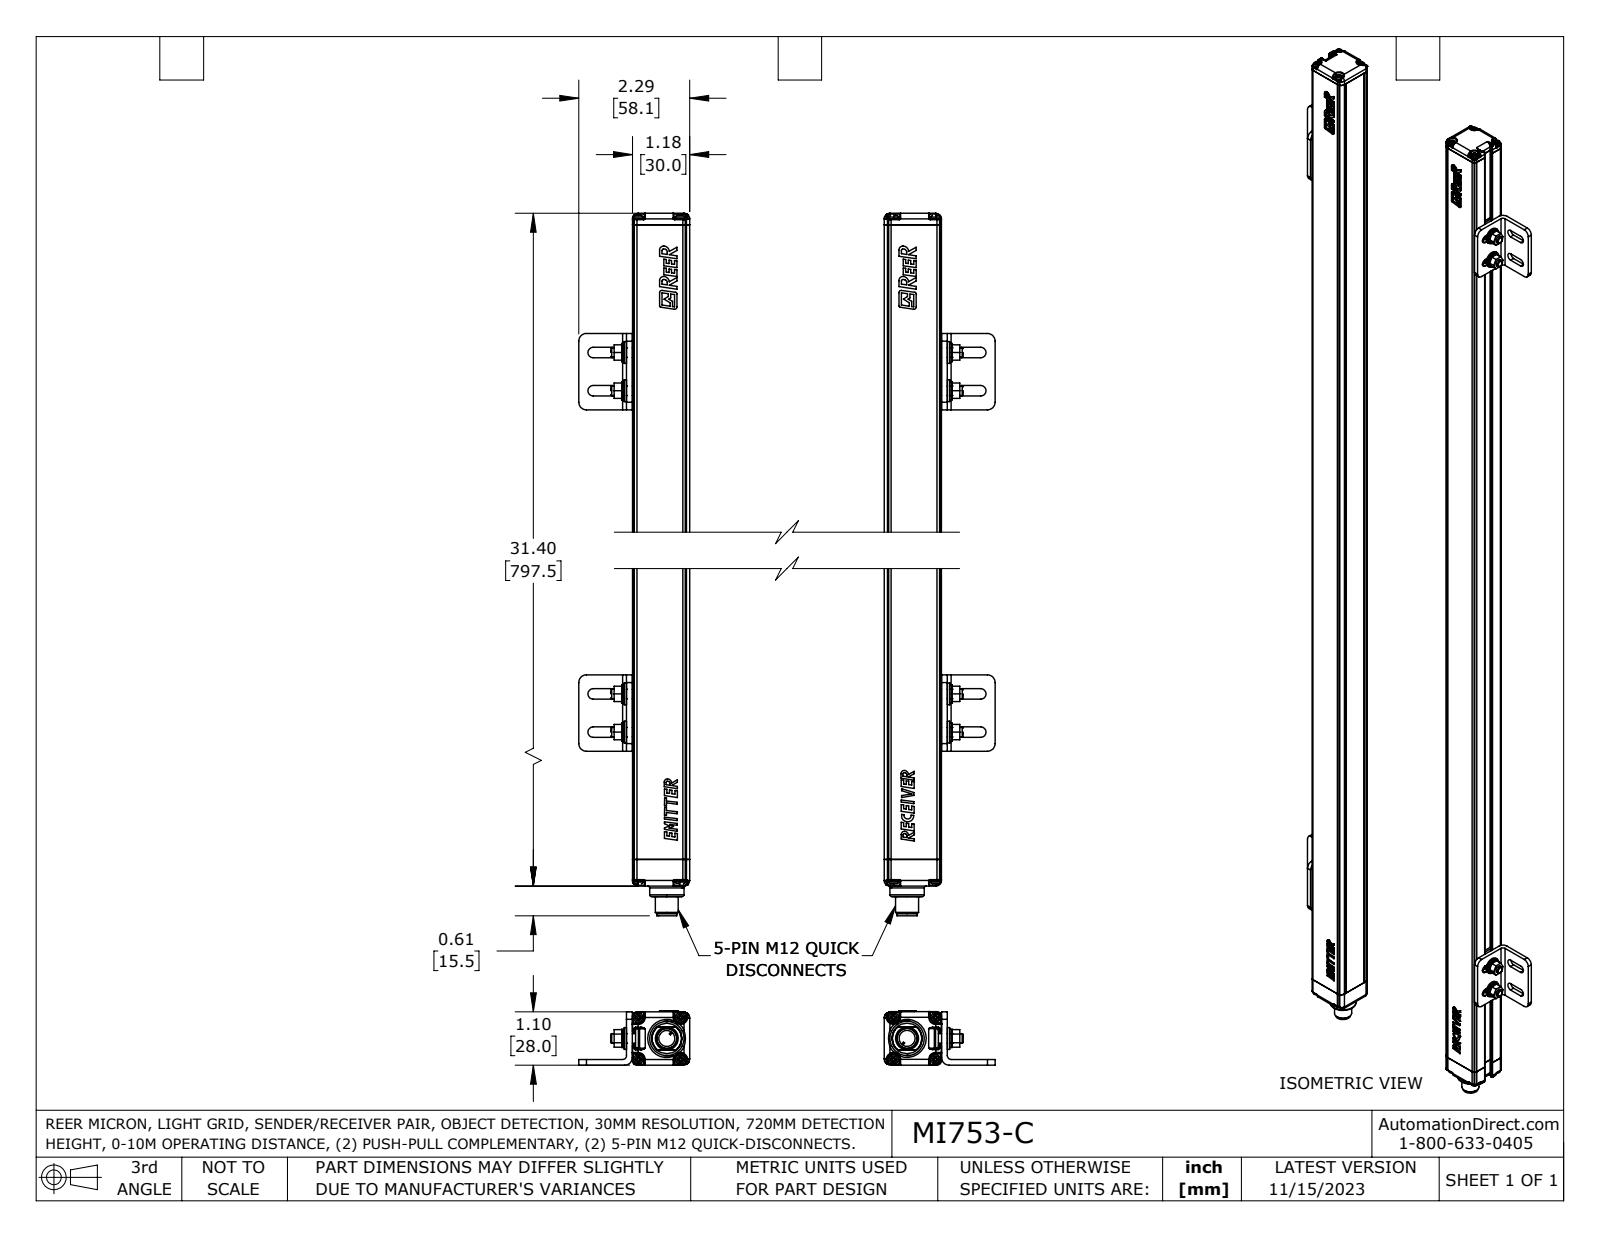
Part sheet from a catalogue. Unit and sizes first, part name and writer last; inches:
Units: inches
Overall size (bounding box): 32.024 × 6.575 × 1.104
Round holes (diameter × count): ⌀0.197 ×16, ⌀0.102 ×8, ⌀0.118 ×8, ⌀0.236 ×8, ⌀0.279 ×8, ⌀0.331 ×2, ⌀0.39 ×2, ⌀0.406 ×2
Round bosses / shafts (diameter × count): ⌀0.047 ×16, ⌀0.026 ×16, ⌀0.45 ×8, ⌀0.381 ×8, ⌀0.138 ×8, ⌀0.098 ×8, ⌀0.709 ×2, ⌀0.472 ×2
Partial cylindrical surfaces — rounded edges, fillets, slot ends (radius × count): R0.02 ×122, R0.01 ×120, R0.016 ×64, R0.016 ×32, R0.108 ×32, R0.004 ×24, R0.118 ×24, R0.157 ×18
Main face-to-face distances: 0.059, 0.846, 0.906, 0.13, 1.102, 2.13, 1.043, 0.138, 2.976, 4.157
Hole centre spacings: 0.787, 0.866, 24.565, 0.513, 0.732, 1.225, 2.704, 3.26
Volume: 29.8 in³ · Surface area: 791 in²
Bodies: 60 solids, 2516 faces (1122 planar, 1014 cylindrical, 380 other)
Part name (STEP PRODUCT): MI751-C_MI753-C_EMITTER; MI751-C_MI753-C; MI751-C_MI753-C_RECEIVER
STEP written by: SolidWorks 2023 (AUTOMOTIVE_DESIGN)
